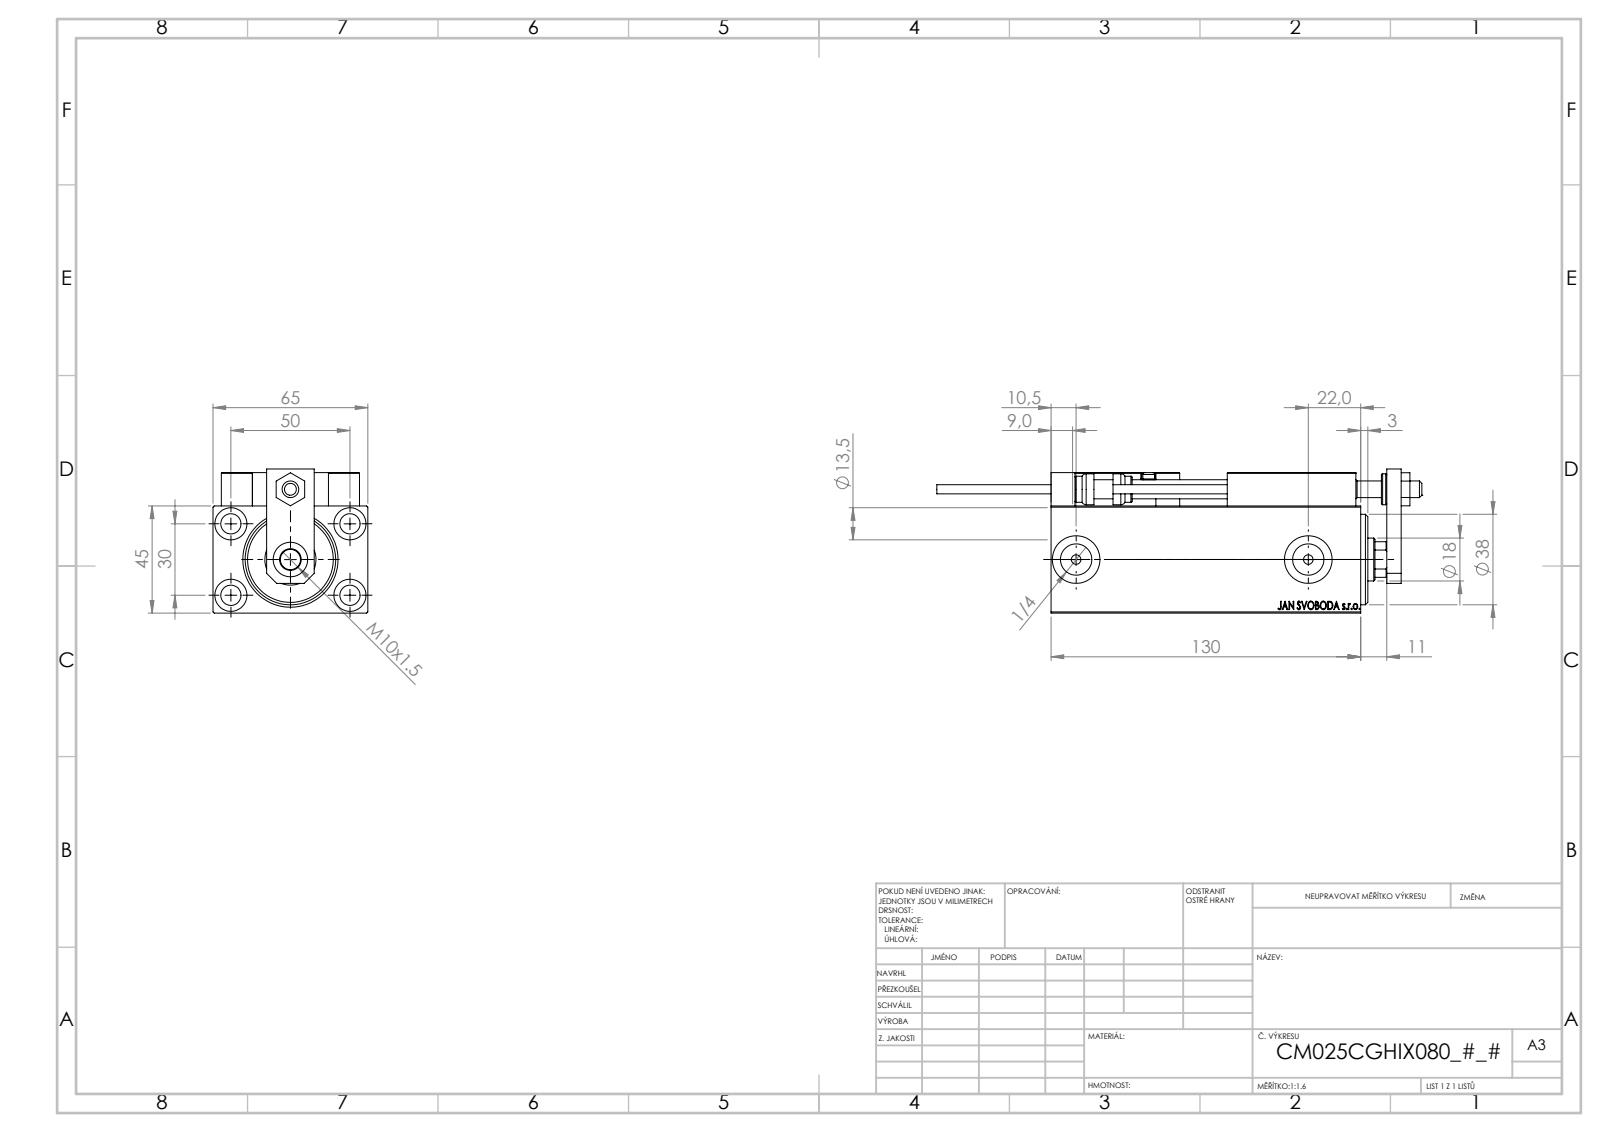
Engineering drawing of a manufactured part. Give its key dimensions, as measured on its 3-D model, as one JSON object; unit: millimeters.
{"part_name": "ZARAZKA; Block; SWITCH X; KONCOVKA (+8 more)", "step_written_by": "SolidWorks 2019 (CONFIG_CONTROL_DESIGN)", "units": "millimeters", "bodies": {"solids": 23, "faces": 1282, "planar": 560, "cylindrical": 188, "other": 534}, "overall_size": [203.7, 65, 60.5], "volume_mm3": 373805, "surface_area_mm2": 99913, "round_holes": [[4, 6], [8, 5], [8.5, 5], [3.2, 4], [13.5, 4], [5, 2], [13.16, 2], [20, 2], [7, 1], [14.5, 1], [18, 1], [21.5, 1]], "round_bosses_or_shafts": [[5, 2], [3.8, 2], [13, 1], [11, 1]], "partial_cylinders_radius": [[0.3, 30], [3, 2], [8.5, 1]], "face_to_face_distances": [45, 65, 14, 6, 59, 3, 13, 3.5, 7, 20], "hole_center_spacings": [29.15, 11.37, 20, 28.9, 29.59, 29.69, 30, 36.06]}
